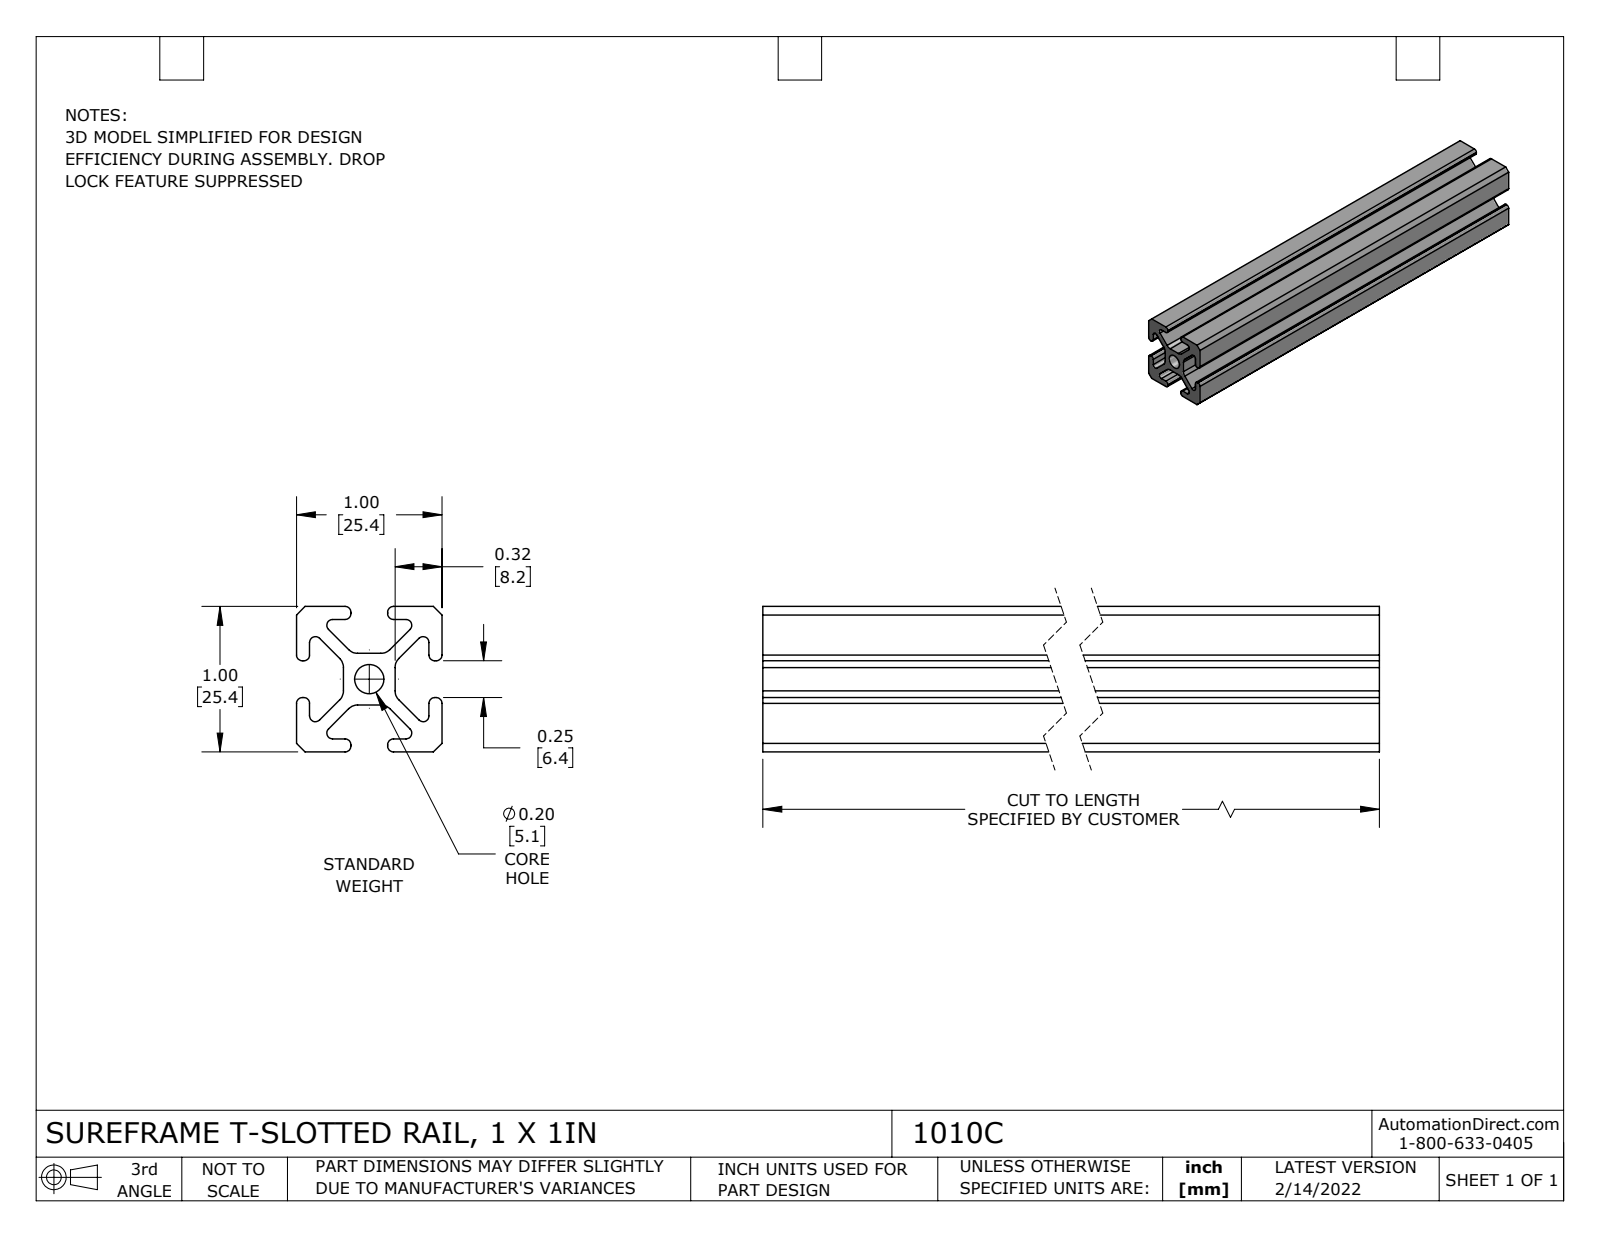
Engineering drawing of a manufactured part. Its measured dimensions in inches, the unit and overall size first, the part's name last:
Units: inches
Overall size (bounding box): 6 × 1 × 1
Round holes (diameter × count): ⌀0.201 ×1
Partial cylindrical surfaces — rounded edges, fillets, slot ends (radius × count): R0.04 ×24, R0.087 ×8
Main face-to-face distances: 1, 0.087, 0.09, 0.91, 0.322, 0.678, 0.233, 0.588, 0.82, 0.622
Volume: 2.696 in³ · Surface area: 51.59 in²
Bodies: 1 solid, 80 faces (42 planar, 38 cylindrical, 0 other)
Part name (STEP PRODUCT): 1010C
STEP written by: SolidWorks 2021 (CONFIG_CONTROL_DESIGN)
